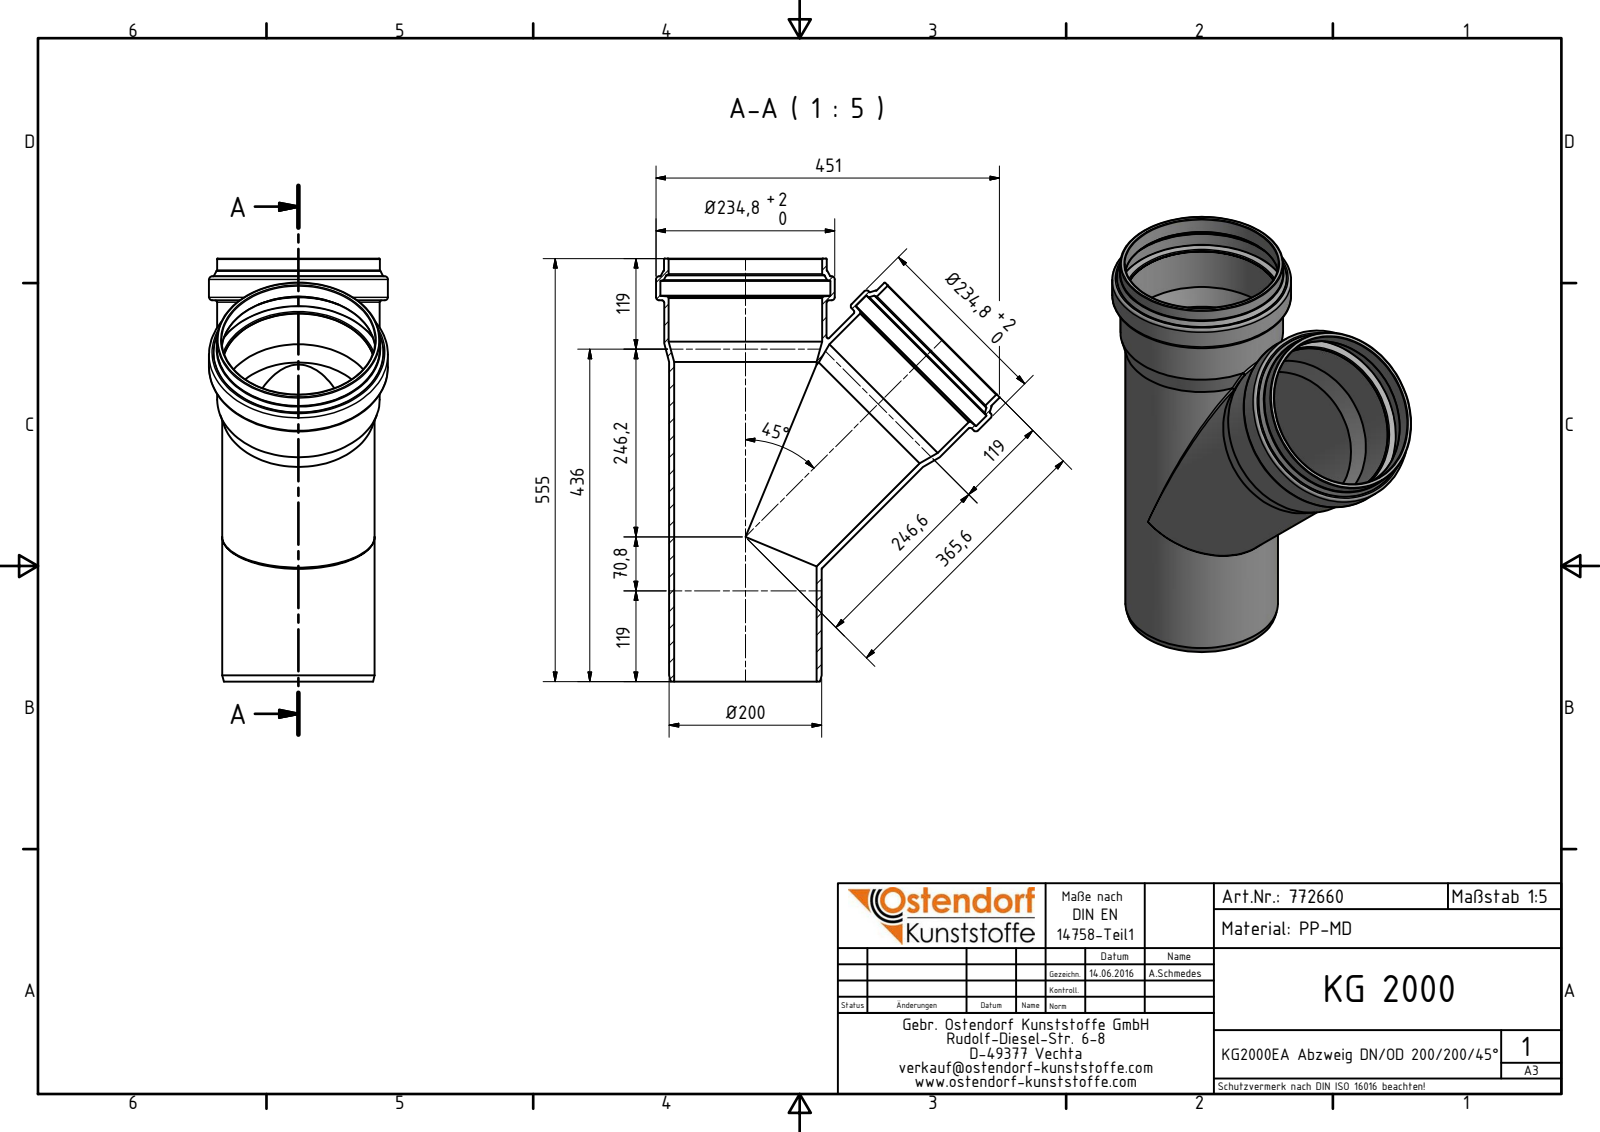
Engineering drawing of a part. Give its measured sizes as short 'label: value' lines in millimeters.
name: 772660 KG2000EA Abzweig DN_OD 200_200_45°
written by: Autodesk Inventor 2016 (AUTOMOTIVE_DESIGN)
unit: mm
bodies: 1 solid, 78 faces (9 planar, 18 cylindrical, 51 other)
size: 555 × 451 × 234.8
volume: 3 080 000 mm³; area: 985 576 mm²
holes: 2× ⌀187.2, 2× ⌀201.5, 2× ⌀201.8, 2× ⌀223
bosses: 2× ⌀234.8, 2× ⌀213.6, 2× ⌀213.3, 2× ⌀200.2
face distances: 500.1, 555, 54.9, 54.89, 23.3, 531.7, 31.6, 31.59, 28.57, 51.87
